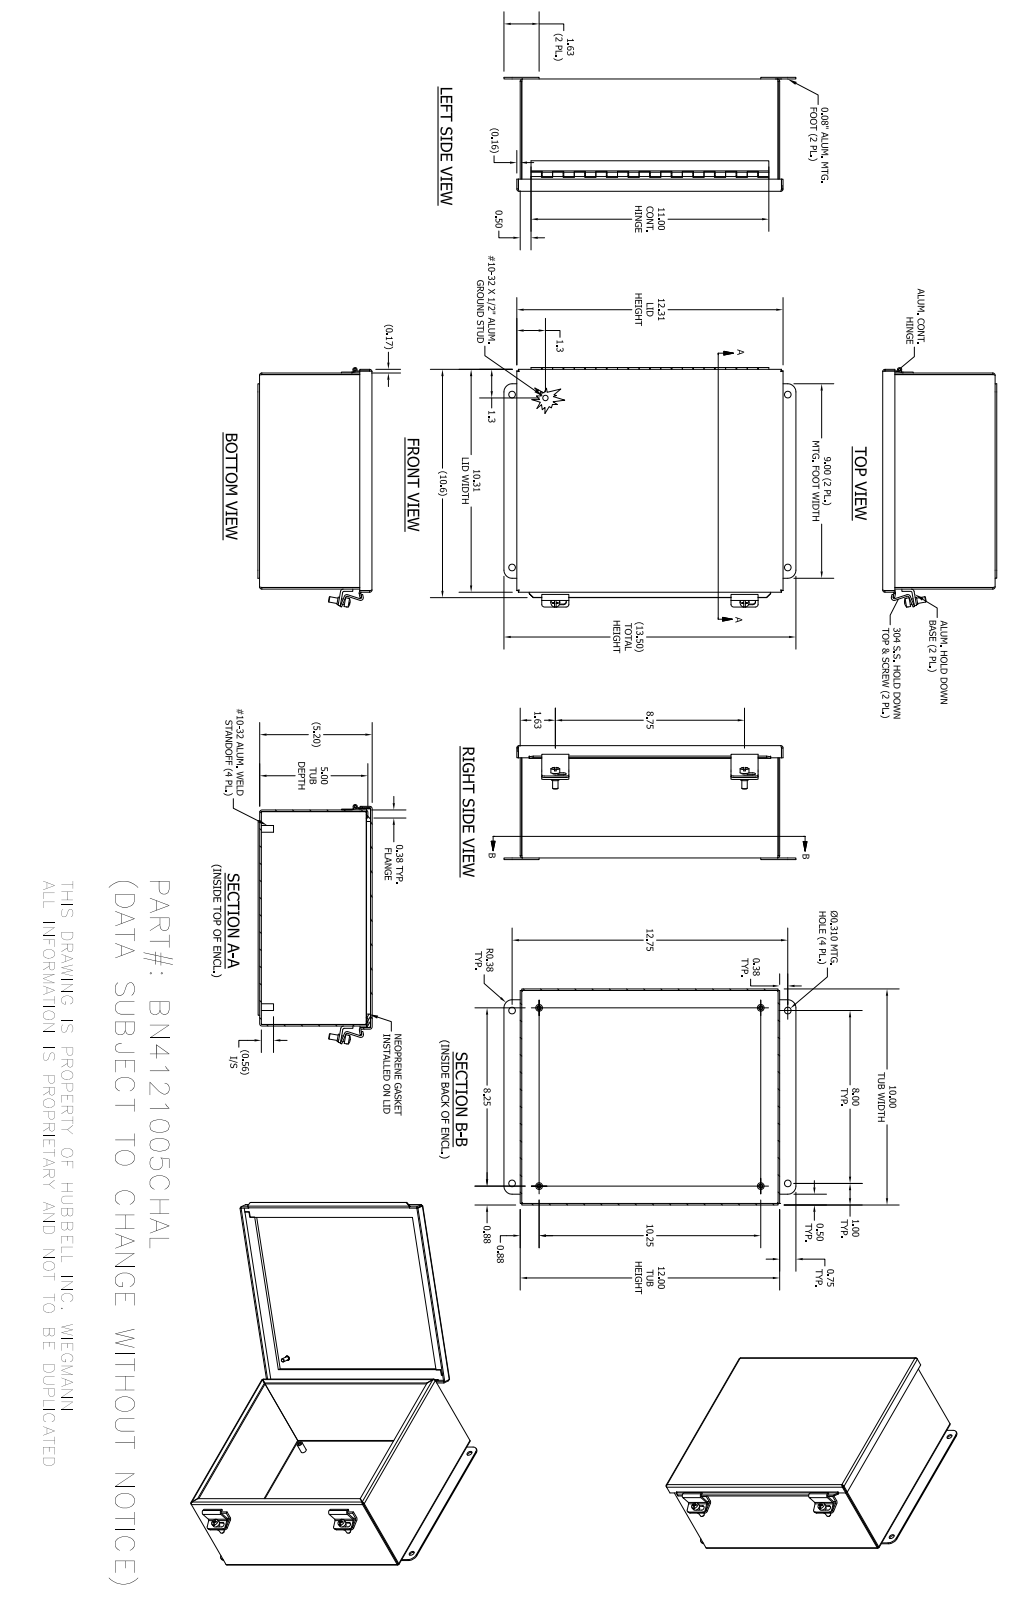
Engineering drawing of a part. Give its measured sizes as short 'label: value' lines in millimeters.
name: B_121005_ALBKP; 32843TH; 32843LH; 32843P (+8 more)
written by: Autodesk Inventor 2016 (AUTOMOTIVE_DESIGN)
unit: mm
bodies: 20 solids, 443 faces (273 planar, 129 cylindrical, 41 other)
size: 342.9 × 281.58 × 133.96
volume: 743 266 mm³; area: 768 647 mm²
holes: 4× ⌀3.97, 4× ⌀6.35, 4× ⌀7.87, 2× ⌀4.98, 1× ⌀2.96
bosses: 5× ⌀6.35, 4× ⌀7.95, 2× ⌀10.4, 2× ⌀8.74, 1× ⌀5.08, 1× ⌀4.83, 1× ⌀2.54
rounds: 13× R0.79, 13× R2.67, 8× R3.17, 4× R3.38, 4× R9.53, 3× R1.6, 3× R3.2
face distances: 1.88, 130.17, 132.05, 128.29, 252.12, 302.92, 254, 250.24, 304.8, 301.04
hole spacings: 209.55, 31.91, 208.8, 208.81, 292.11, 292.12, 357.64, 357.65
